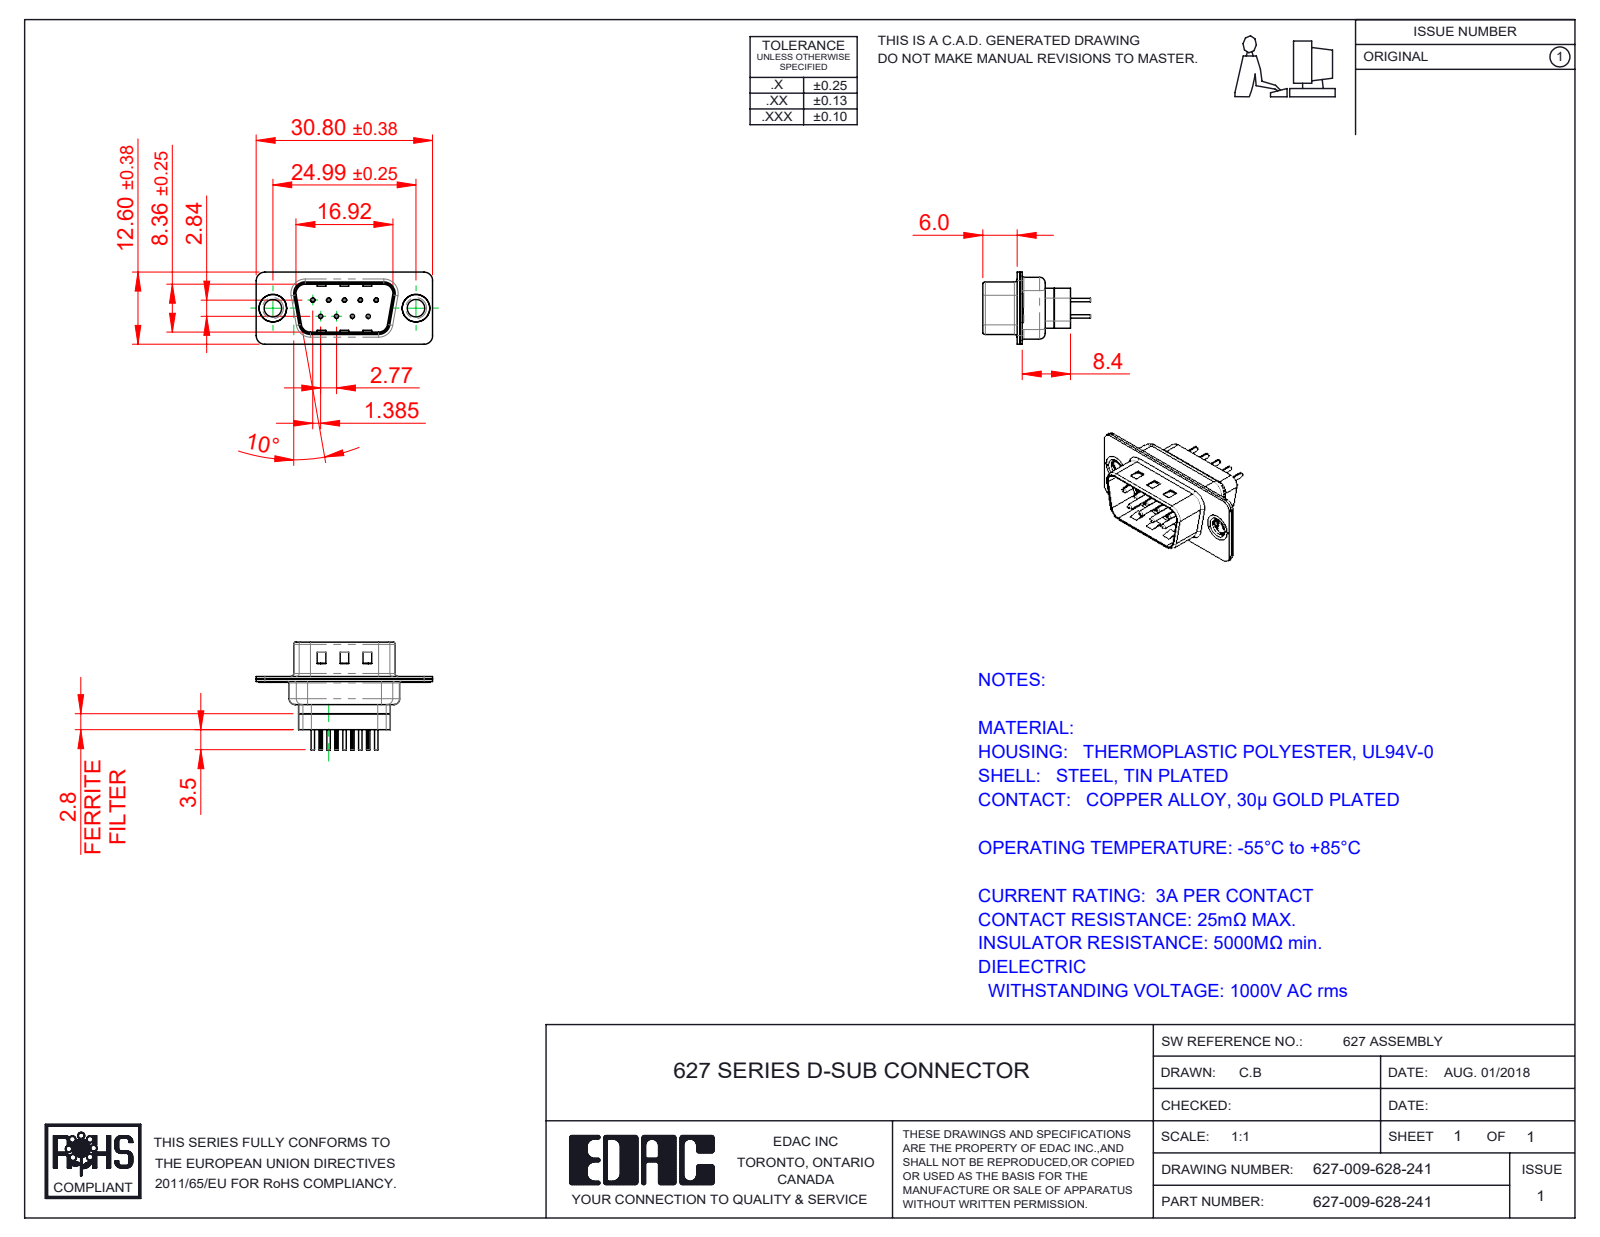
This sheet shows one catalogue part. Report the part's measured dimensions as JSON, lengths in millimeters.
{"part_name": "627 Contact Row 1_28L; 627 Shell Rear_09 Contacts; 627 Thru Hole Rivet; 627-009-628-241 (+3 more)", "step_written_by": "SolidWorks 2020 (CONFIG_CONTROL_DESIGN)", "units": "millimeters", "bodies": {"solids": 15, "faces": 1189, "planar": 329, "cylindrical": 469, "other": 391}, "overall_size": [30.8, 18.8, 12.6], "volume_mm3": 1482, "surface_area_mm2": 4247, "round_holes": [[0.2, 9], [0.35, 9], [1.1, 9], [1.6, 9], [3.05, 2], [4, 2], [4.8, 2]], "round_bosses_or_shafts": [[2, 9], [1.5, 9], [0.75, 9], [0.6, 9], [5, 2], [4.9, 2], [3.55, 2]], "partial_cylinders_radius": [[0.1, 18], [1.5, 18], [2, 12], [0.5, 8], [1.6, 8], [0.25, 4], [0.6, 4], [0.65, 4]], "face_to_face_distances": [0.45, 0.4, 0.9, 6.5, 5.6, 6.05, 0.82, 9.58, 8.4, 1.4], "hole_center_spacings": [3.16, 2.77, 5.54, 5.03, 5.04, 8.31, 7.48, 7.49]}
